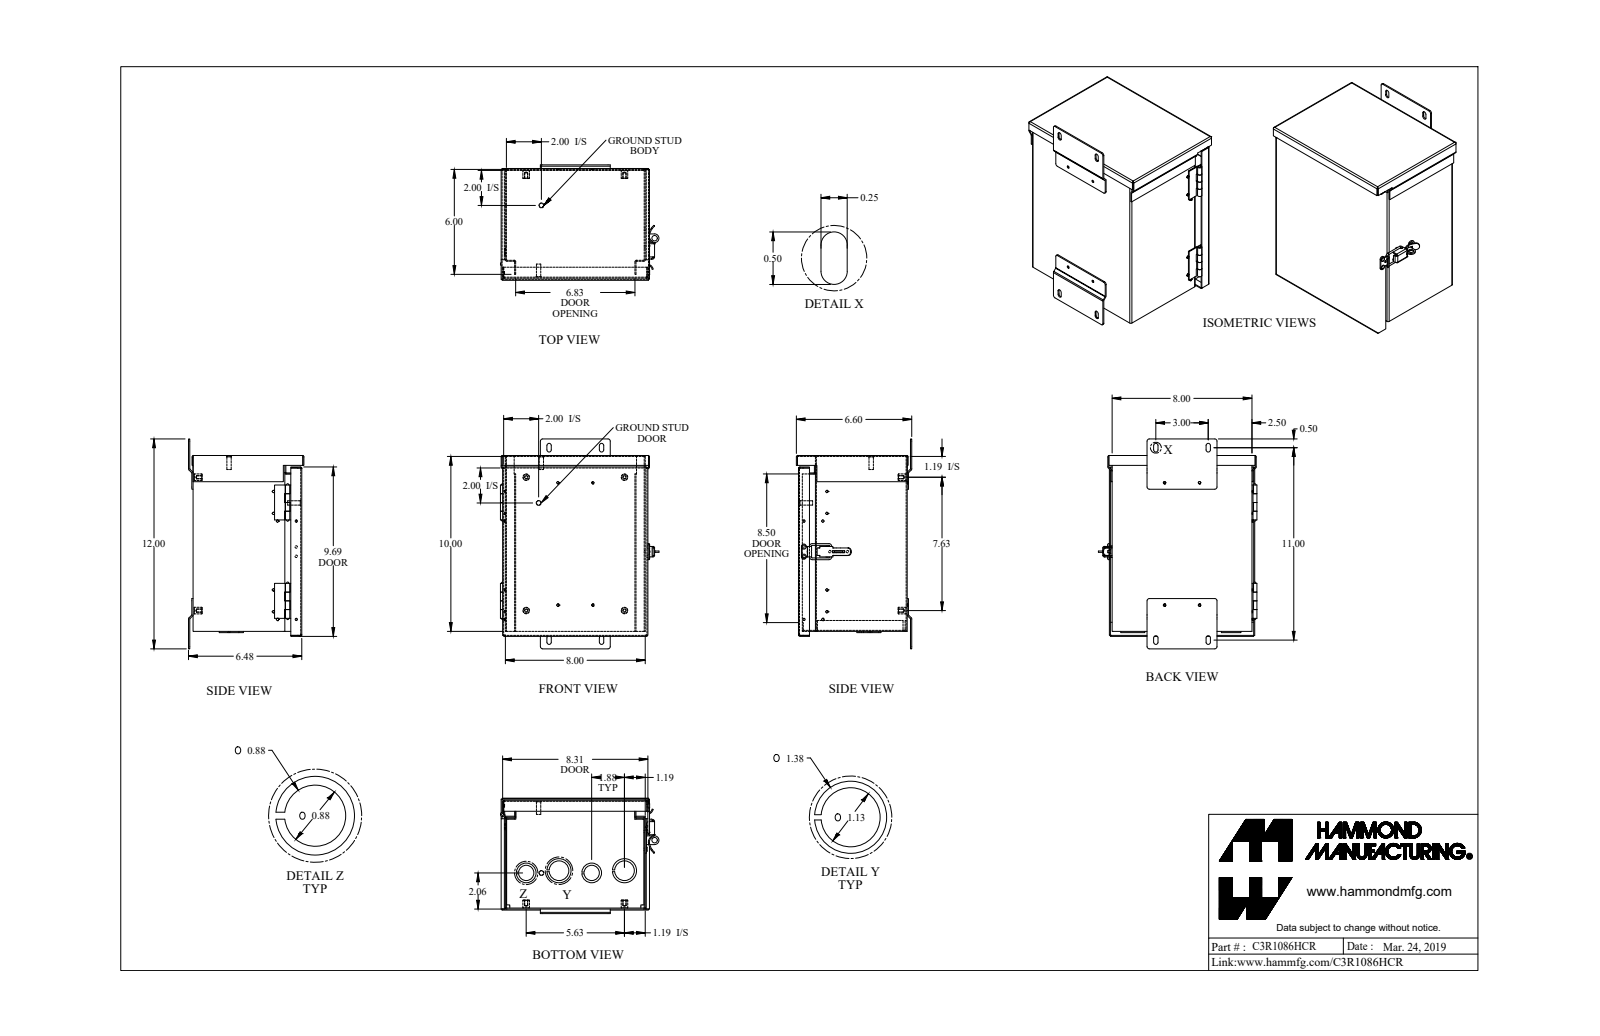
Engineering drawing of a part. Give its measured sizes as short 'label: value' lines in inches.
name: C3R1086HCR_Default
written by: SolidWorks 2019 (CONFIG_CONTROL_DESIGN)
unit: in
bodies: 31 solids, 846 faces (496 planar, 295 cylindrical, 55 other)
size: 12 × 9.07 × 6.599
volume: 33.69 in³; area: 1 081 in²
holes: 4× ⌀0.137, 4× ⌀0.14, 4× ⌀0.156, 2× ⌀0.133, 2× ⌀0.145, 2× ⌀1.125, 1× ⌀0.125, 1× ⌀0.13, 1× ⌀0.313, 1× ⌀0.875, 1× ⌀0.875
bosses: 12× ⌀0.131, 4× ⌀0.375, 4× ⌀0.1, 3× ⌀0.125, 2× ⌀1.375, 2× ⌀1.125, 2× ⌀0.281, 2× ⌀0.25
rounds: 28× R0.029, 28× R0.086, 21× R0.125, 6× R0.036, 6× R0.108, 2× R0.135, 1× R0.04, 1× R0.068
face distances: 0.057, 6.16, 7.943, 10, 6.103, 6.217, 8, 0.187, 0.244, 7.886
hole spacings: 1.498, 1.01, 1.01, 1.839, 1.84, 1.88, 2, 2.498
